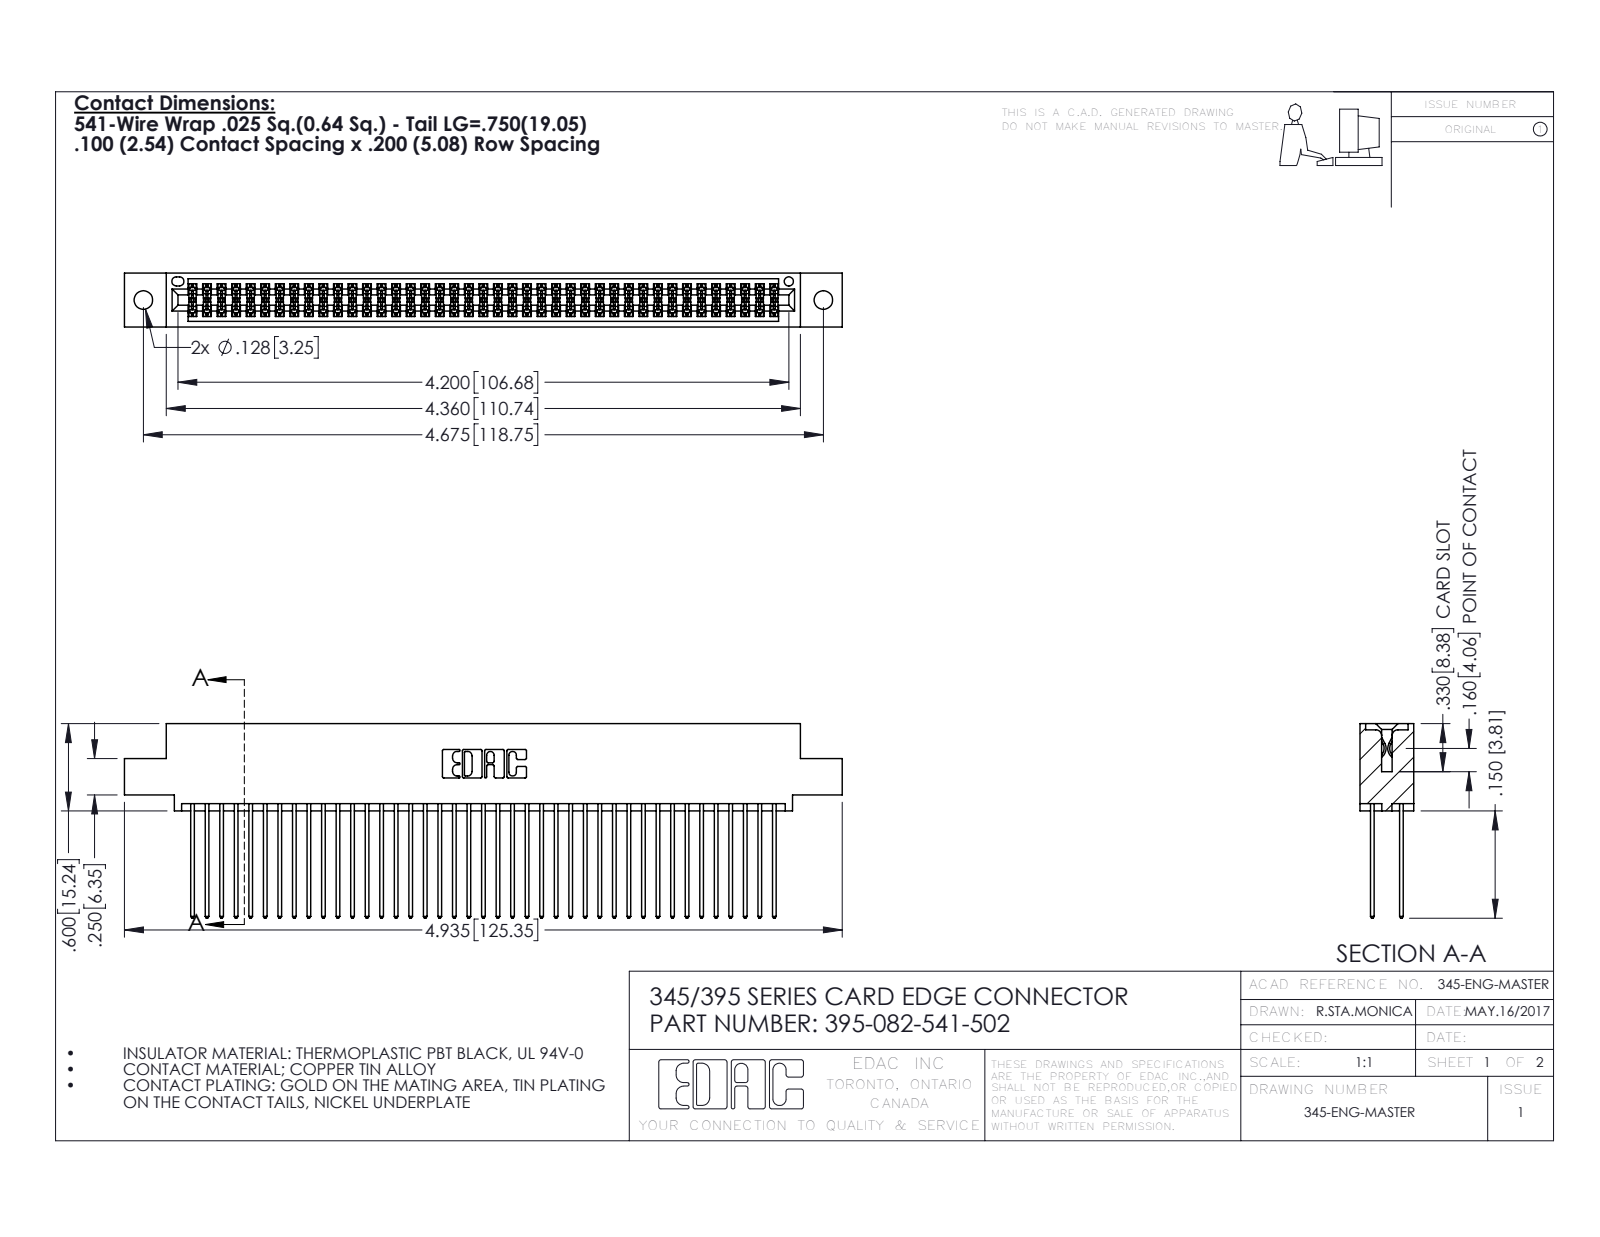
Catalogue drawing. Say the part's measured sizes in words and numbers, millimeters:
The part is named "395-082-541-502; 345-292-001_345-293-141; 345 Part_0.110 Offset - 0.128 Dia". Its 3-D file was written by "SolidWorks 2016 (CONFIG_CONTROL_DESIGN)". It is 83 solids with 4230 faces: 2790 planar, 1440 cylindrical and 0 other. Overall it measures 125.3 by 34 by 9.4 millimeters. Its volume is 12 500 cubic millimeters and its surface area 20 530 square millimeters. Round holes: 2 of diameter 3.3, 1 of diameter 1.6. Partial cylindrical surfaces (rounded edges, fillets, slot ends): 123 of radius 0.2, 82 of radius 0.3, 22 of radius 0.3, 6 of radius 0.2, 6 of radius 0.8, 3 of radius 0.7, 2 of radius 0.4, 2 of radius 0.5. The main face-to-face distances are 7.6, 1.8, 5.1, 2.5, 6.9, 0.6, 5.7, 9.4, 4.4, 3.8. The hole center spacings are 6.9, 112.8, 118.7.
